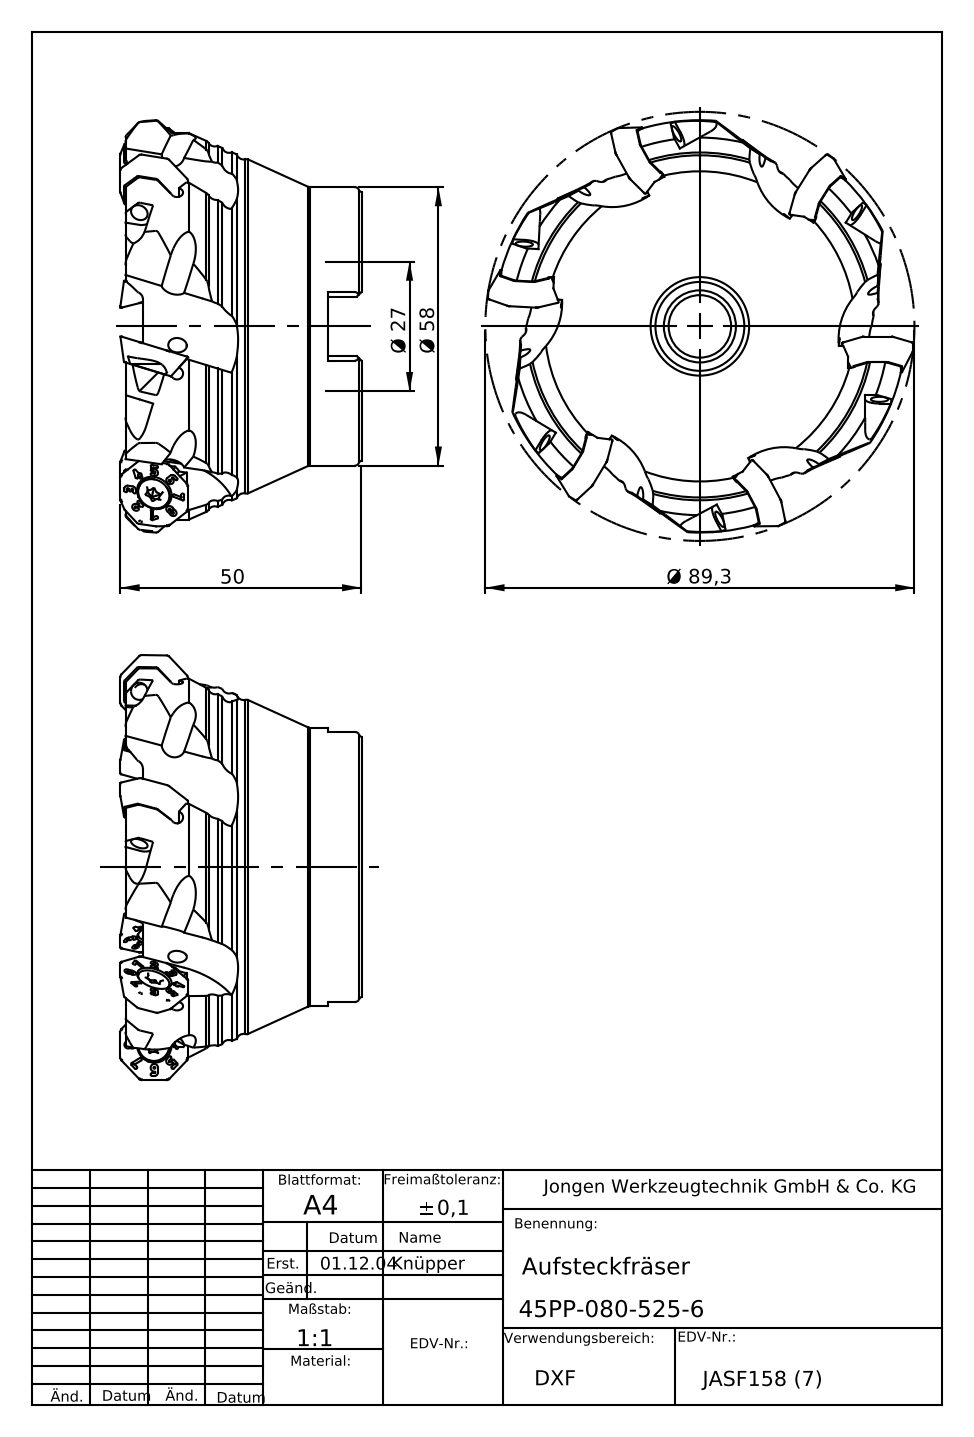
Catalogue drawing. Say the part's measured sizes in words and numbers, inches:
The part is named "45PP-080-525-6". Its 3-D file was written by "SolidWorks 2016 (AUTOMOTIVE_DESIGN)". It is 1 solid with 215 faces: 59 planar, 50 cylindrical and 106 other. Overall it measures 3.512 by 3.512 by 1.967 inches. Its volume is 9.933 cubic inches and its surface area 42.39 square inches. Round holes: 6 of diameter 0.118, 1 of diameter 0.512, 1 of diameter 0.728, 1 of diameter 1.063, 1 of diameter 1.069, 1 of diameter 1.075. Round bosses or shafts: 1 of diameter 2.283. Partial cylindrical surfaces (rounded edges, fillets, slot ends): 6 of radius 0.049, 6 of radius 0.098, 6 of radius 0.492, 1 of radius 1.583. The main face-to-face distances are 1.791, 0.276, 1.516, 0.984, 0.709, 0.807, 0.488, 1.28, 1.004, 0.295.
